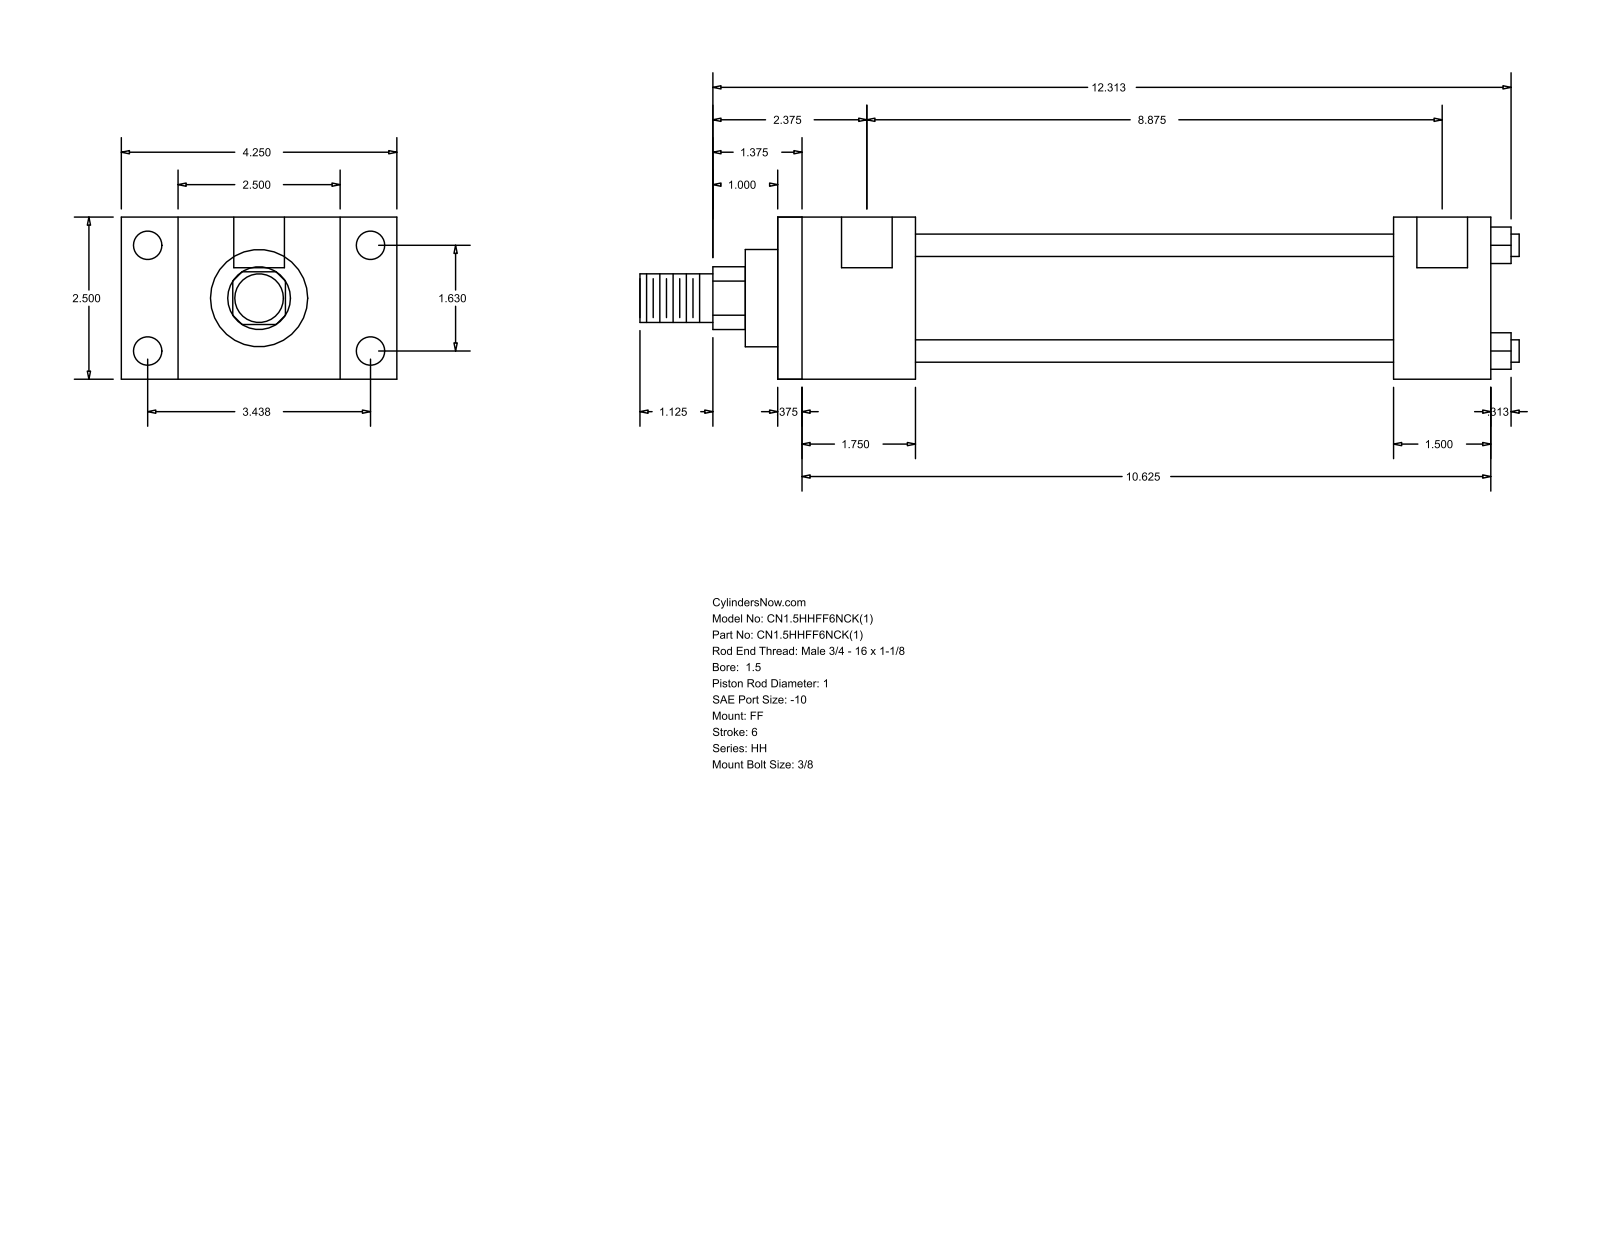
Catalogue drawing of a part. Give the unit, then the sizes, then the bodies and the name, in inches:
Units: inches
Overall size (bounding box): 13.563 × 4.25 × 2.5
Round holes (diameter × count): ⌀0.219 ×4, ⌀0.438 ×4, ⌀0.781 ×2
Round bosses / shafts (diameter × count): ⌀0.345 ×4, ⌀1.75 ×1, ⌀1.5 ×1, ⌀1 ×1, ⌀0.75 ×1
Partial cylindrical surfaces — rounded edges, fillets, slot ends (radius × count): R0.484 ×1
Main face-to-face distances: 2.5, 11, 0.375, 10.625, 1.5, 2.125, 1.75, 8.875, 9.5, 9.125
Hole centre spacings: 0.063, 1.63, 3.438, 3.805, 8.937, 9, 8.875
Bodies: 0 solids, 92 faces (64 planar, 28 cylindrical, 0 other)
Part name (STEP PRODUCT): HH_FF__0150_1
STEP written by: GSSL Pune (CONFIG_CONTROL_DESIGN)
